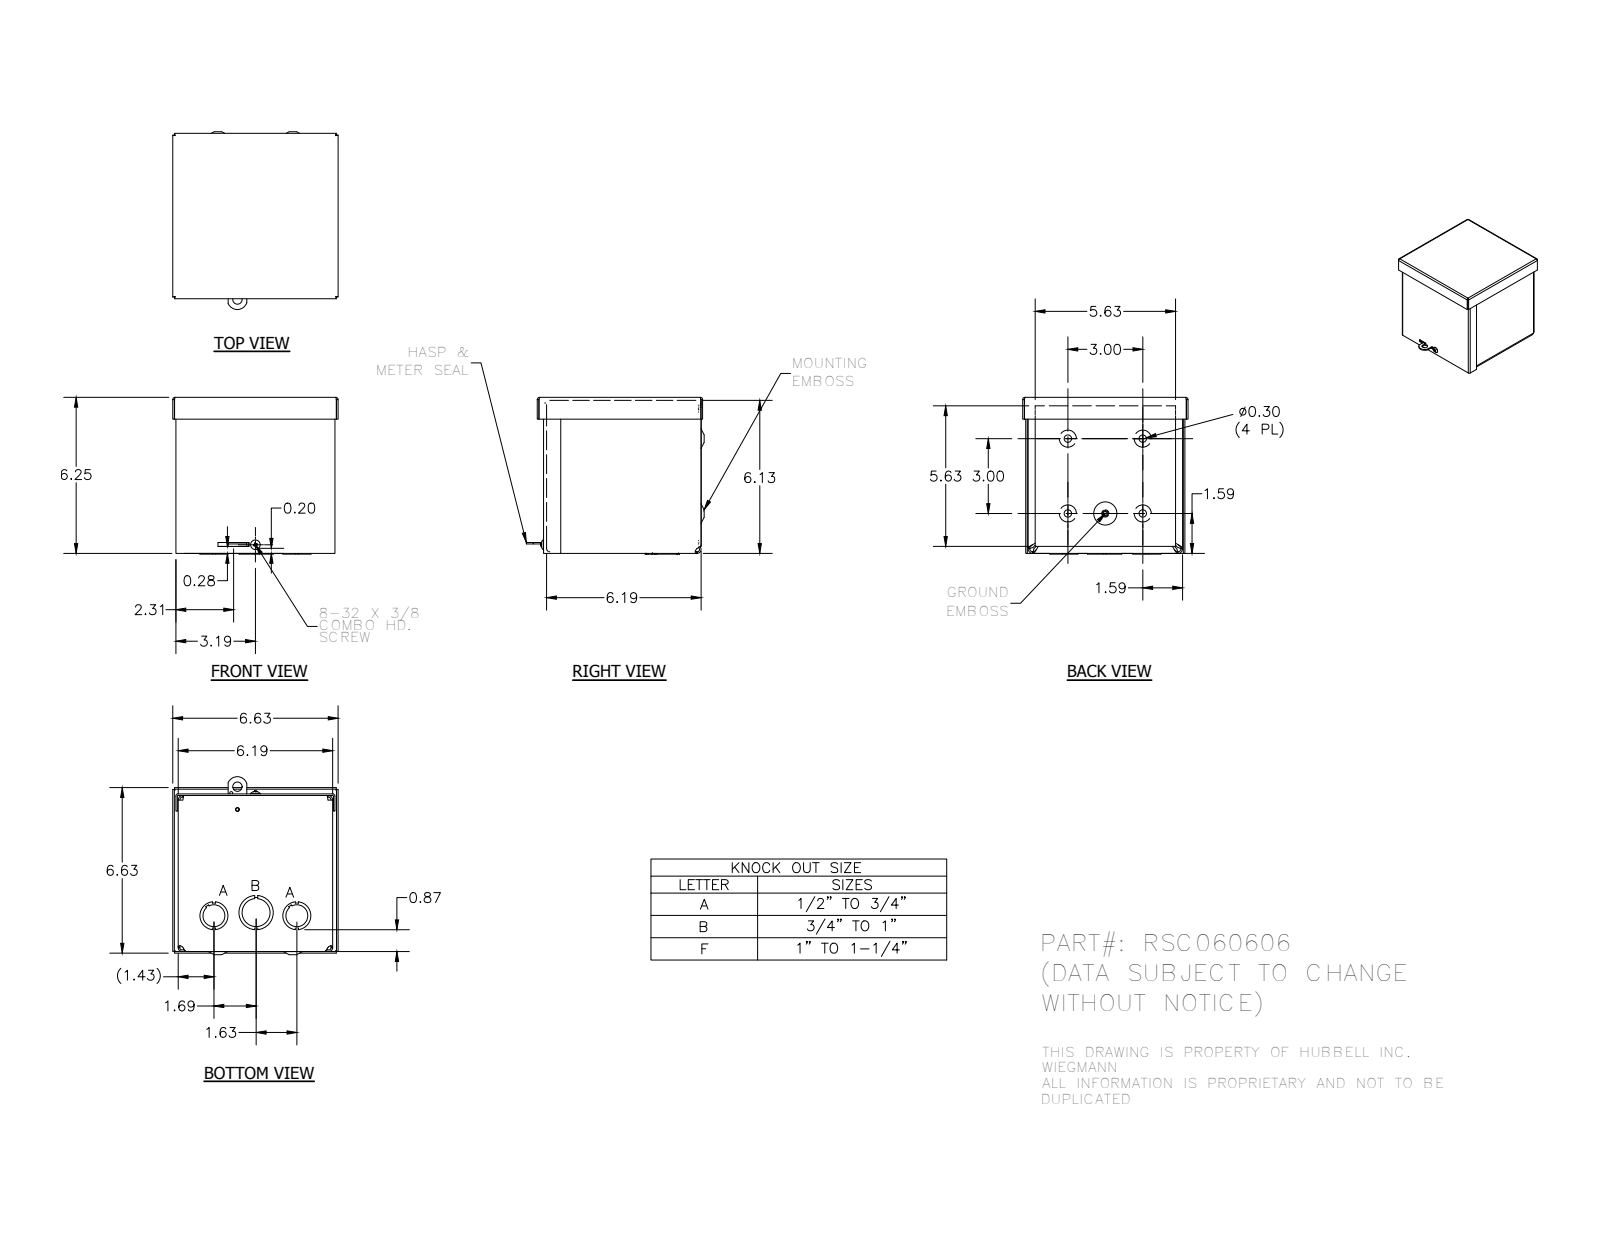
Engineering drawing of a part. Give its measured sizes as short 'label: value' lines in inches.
name: RSC060606; RSC060606_WRAP; RSC0606_LID; RSC0606_CAP (+4 more)
written by: Autodesk Inventor 2012 (AUTOMOTIVE_DESIGN)
unit: in
bodies: 6 solids, 461 faces (220 planar, 116 cylindrical, 125 other)
size: 7.125 × 6.625 × 6.281
volume: 20.14 in³; area: 661.7 in²
holes: 4× ⌀0.3, 3× ⌀1.125, 2× ⌀0.125, 2× ⌀0.313, 2× ⌀0.875, 1× ⌀0.148, 1× ⌀0.156, 1× ⌀0.165, 1× ⌀0.375, 1× ⌀1.375
bosses: 1× ⌀0.384, 1× ⌀0.229, 1× ⌀0.164
rounds: 10× R0.01, 8× R0.031, 8× R0.093, 8× R0.125, 8× R0.187, 4× R0.021, 4× R0.031, 4× R0.055
face distances: 0.062, 6.126, 0.062, 6.188, 6.25, 0.124, 6.187, 6.249, 6.063, 6.187
hole spacings: 3, 1.5, 3.354, 4.243, 0.358, 0.702, 0.913, 1.252
